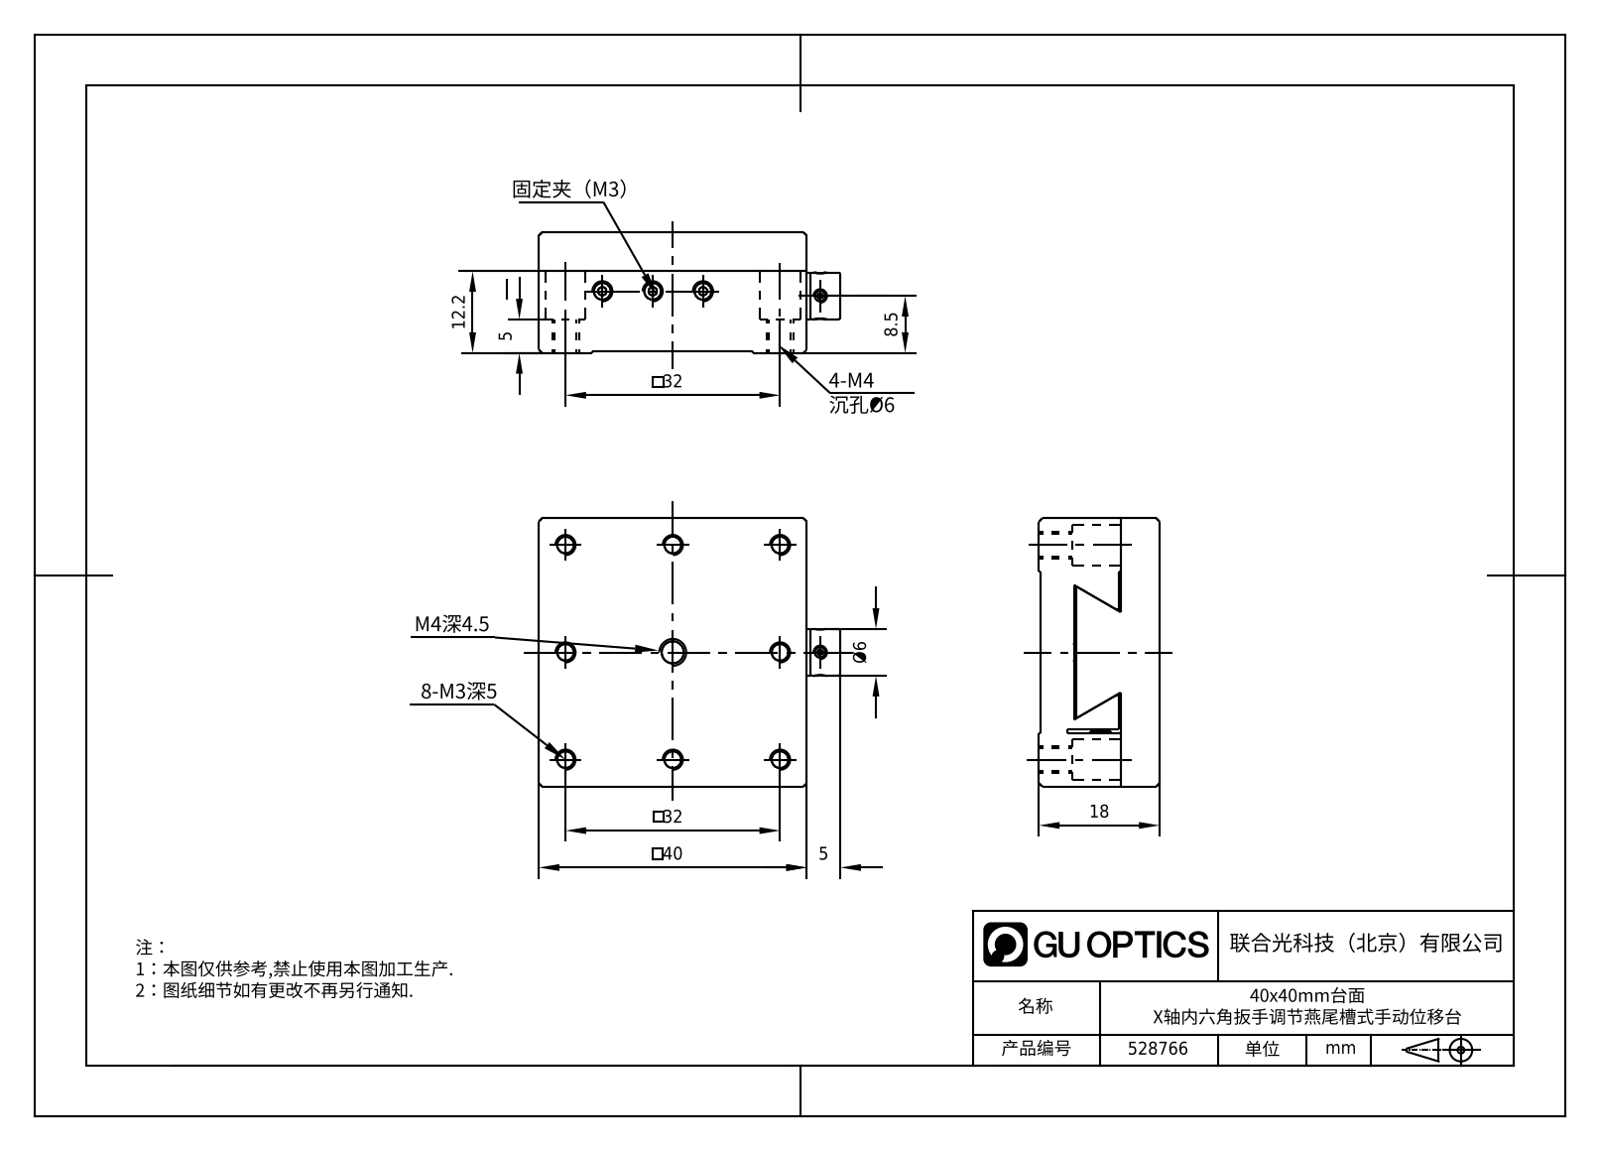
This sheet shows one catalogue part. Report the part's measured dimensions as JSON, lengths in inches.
{"part_name": "528766", "step_written_by": "SolidWorks 2020 (AUTOMOTIVE_DESIGN)", "units": "inches", "bodies": {"solids": 3, "faces": 118, "planar": 76, "cylindrical": 31, "other": 11}, "overall_size": [1.732, 1.575, 0.709], "volume_in3": 1.522, "surface_area_in2": 20.18, "round_holes": [[0.097, 9], [0.13, 4], [0.236, 4], [0.097, 3], [0.128, 1], [0.157, 1]], "round_bosses_or_shafts": [[0.236, 1], [0.197, 1], [0.118, 1]], "partial_cylinders_radius": [[0.079, 3], [0.098, 2]], "face_to_face_distances": [0.236, 0.689, 1.575, 0.453, 0.472, 0.228, 0.465, 0.217, 0.224, 0.244], "hole_center_spacings": [0.63, 0.891, 1.409, 1.26, 0.276, 1.781, 0.551]}
